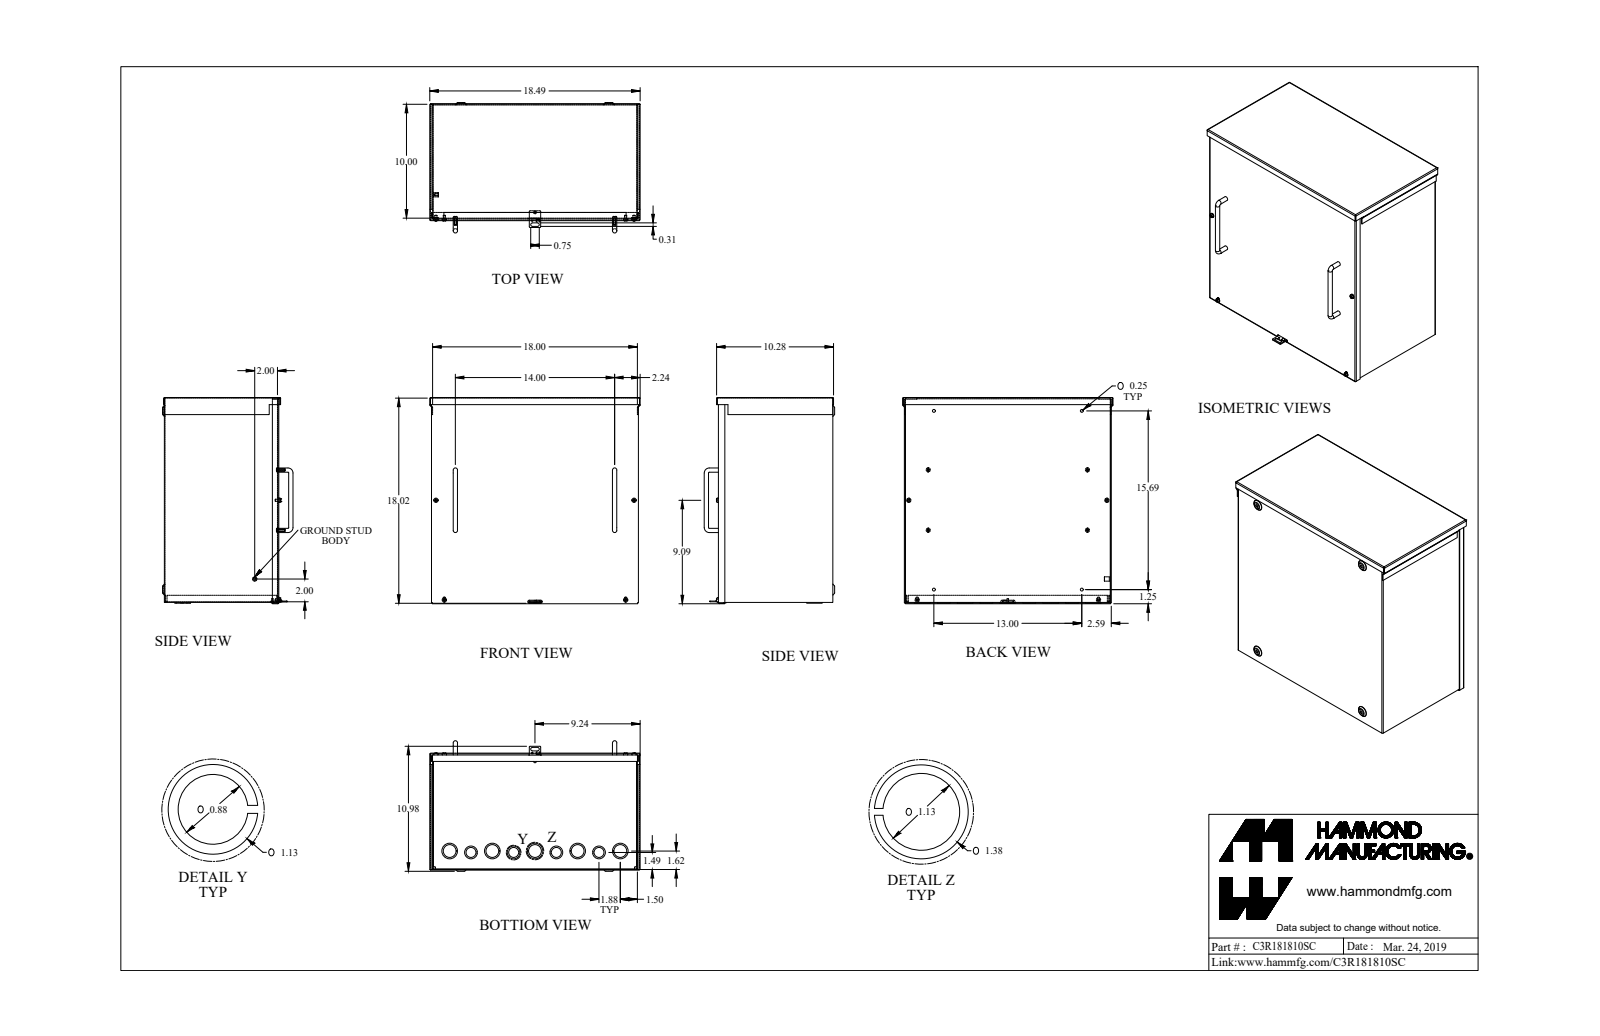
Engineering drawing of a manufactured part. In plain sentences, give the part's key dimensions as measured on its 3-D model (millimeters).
The part is named "C3R181810SC_Default". Its 3-D file was written by "SolidWorks 2019 (CONFIG_CONTROL_DESIGN)". It is 17 solids with 609 faces: 314 planar, 177 cylindrical and 118 other. Overall it measures 469.6 by 460.2 by 291.2 millimeters. Its volume is 1 435 000 cubic millimeters and its surface area 1 966 000 square millimeters. Round holes: 5 of diameter 4, 4 of diameter 4.3, 4 of diameter 5.2, 4 of diameter 6.4, 3 of diameter 28.6, 2 of diameter 22.2, 2 of diameter 22.2, 2 of diameter 28.6, 1 of diameter 3.2, 1 of diameter 3.5. Round bosses or shafts: 9 of diameter 9.5, 8 of diameter 4.8, 5 of diameter 34.9, 4 of diameter 28.6, 4 of diameter 9.3, 2 of diameter 9.5, 1 of diameter 3.2. Partial cylindrical surfaces (rounded edges, fillets, slot ends): 21 of radius 0.7, 21 of radius 2.2, 8 of radius 2.8, 8 of radius 3.2, 2 of radius 4. The main face-to-face distances are 1.4, 254, 455.8, 457.2, 252.6, 255.4, 1.4, 454.3, 454.3, 455.8. The hole center spacings are 355.6, 95.3, 0.5, 47.7, 47.8, 80.1, 132.6, 134.6.
